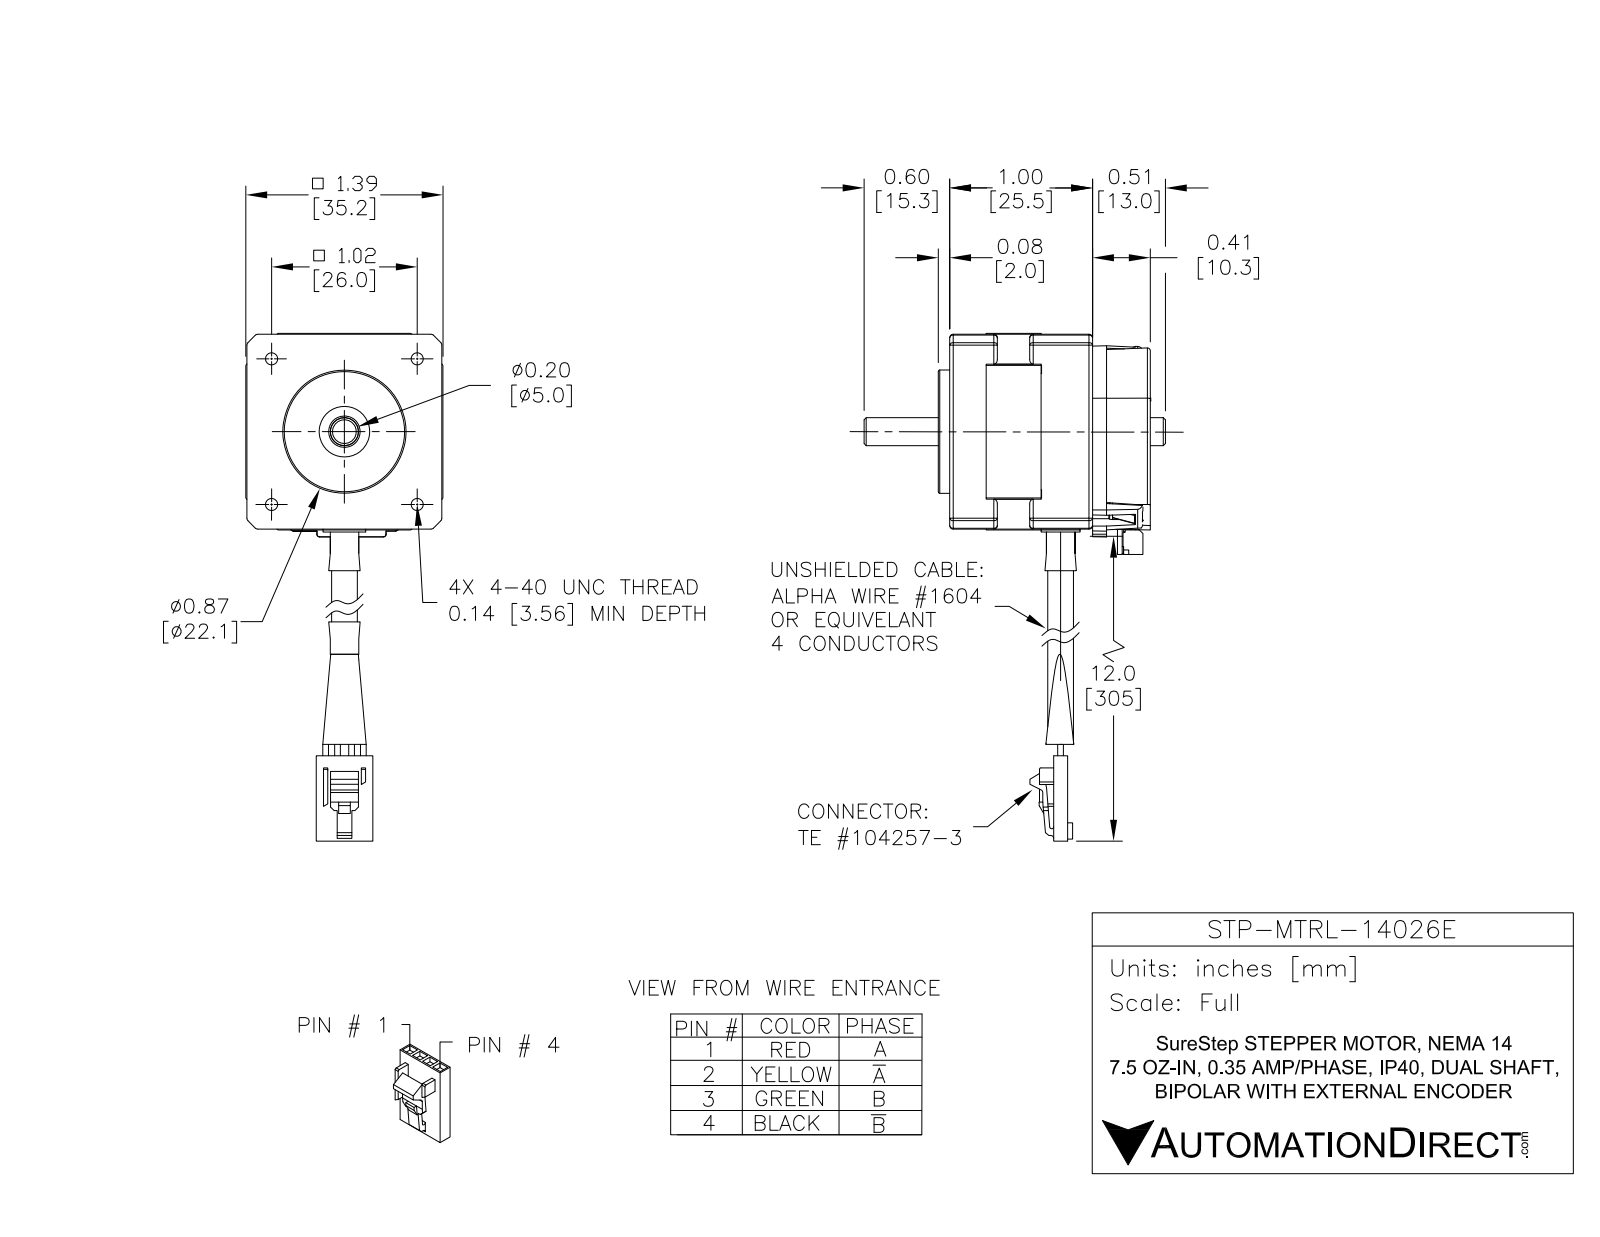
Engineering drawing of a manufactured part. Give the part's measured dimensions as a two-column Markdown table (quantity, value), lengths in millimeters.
| quantity | value |
| --- | --- |
| part name | STP-MTRL-14026E |
| STEP written by | SolidWorks 2017 (AUTOMOTIVE_DESIGN) |
| units | millimeters |
| bodies | 17 solids, 1781 faces (1002 planar, 458 cylindrical, 321 other) |
| overall size | 341.6 × 53.8 × 35.1 |
| volume | 25 790 mm³ |
| surface area | 29 750 mm² |
| round holes (diameter × count) | 2 × 6, 0.8 × 4, 0.9 × 4, 5.7 × 4, 1.7 × 2, 2.2 × 2, 2.2 × 2, 2.3 × 2, 2.9 × 2, 4.1 × 2, 4.5 × 2, 5 × 1 |
| round bosses / shafts (diameter × count) | 1.5 × 4, 1 × 4, 5.2 × 3, 1.3 × 2, 22 × 1, 18.3 × 1, 12.1 × 1, 11.8 × 1 |
| partial cylindrical surfaces (radius × count) | 0.6 × 24, 1 × 22, 0.5 × 10, 0.5 × 6, 1 × 6, 2 × 6, 0.3 × 4, 0.4 × 4 |
| main face-to-face distances | 34.8, 35, 35.8, 31.5, 1.7, 33.1, 2.6, 30.8, 25.5, 22.9 |
| hole center spacings | 22.4, 26, 5.7, 9, 12.7, 13.5, 18, 18.4 |
